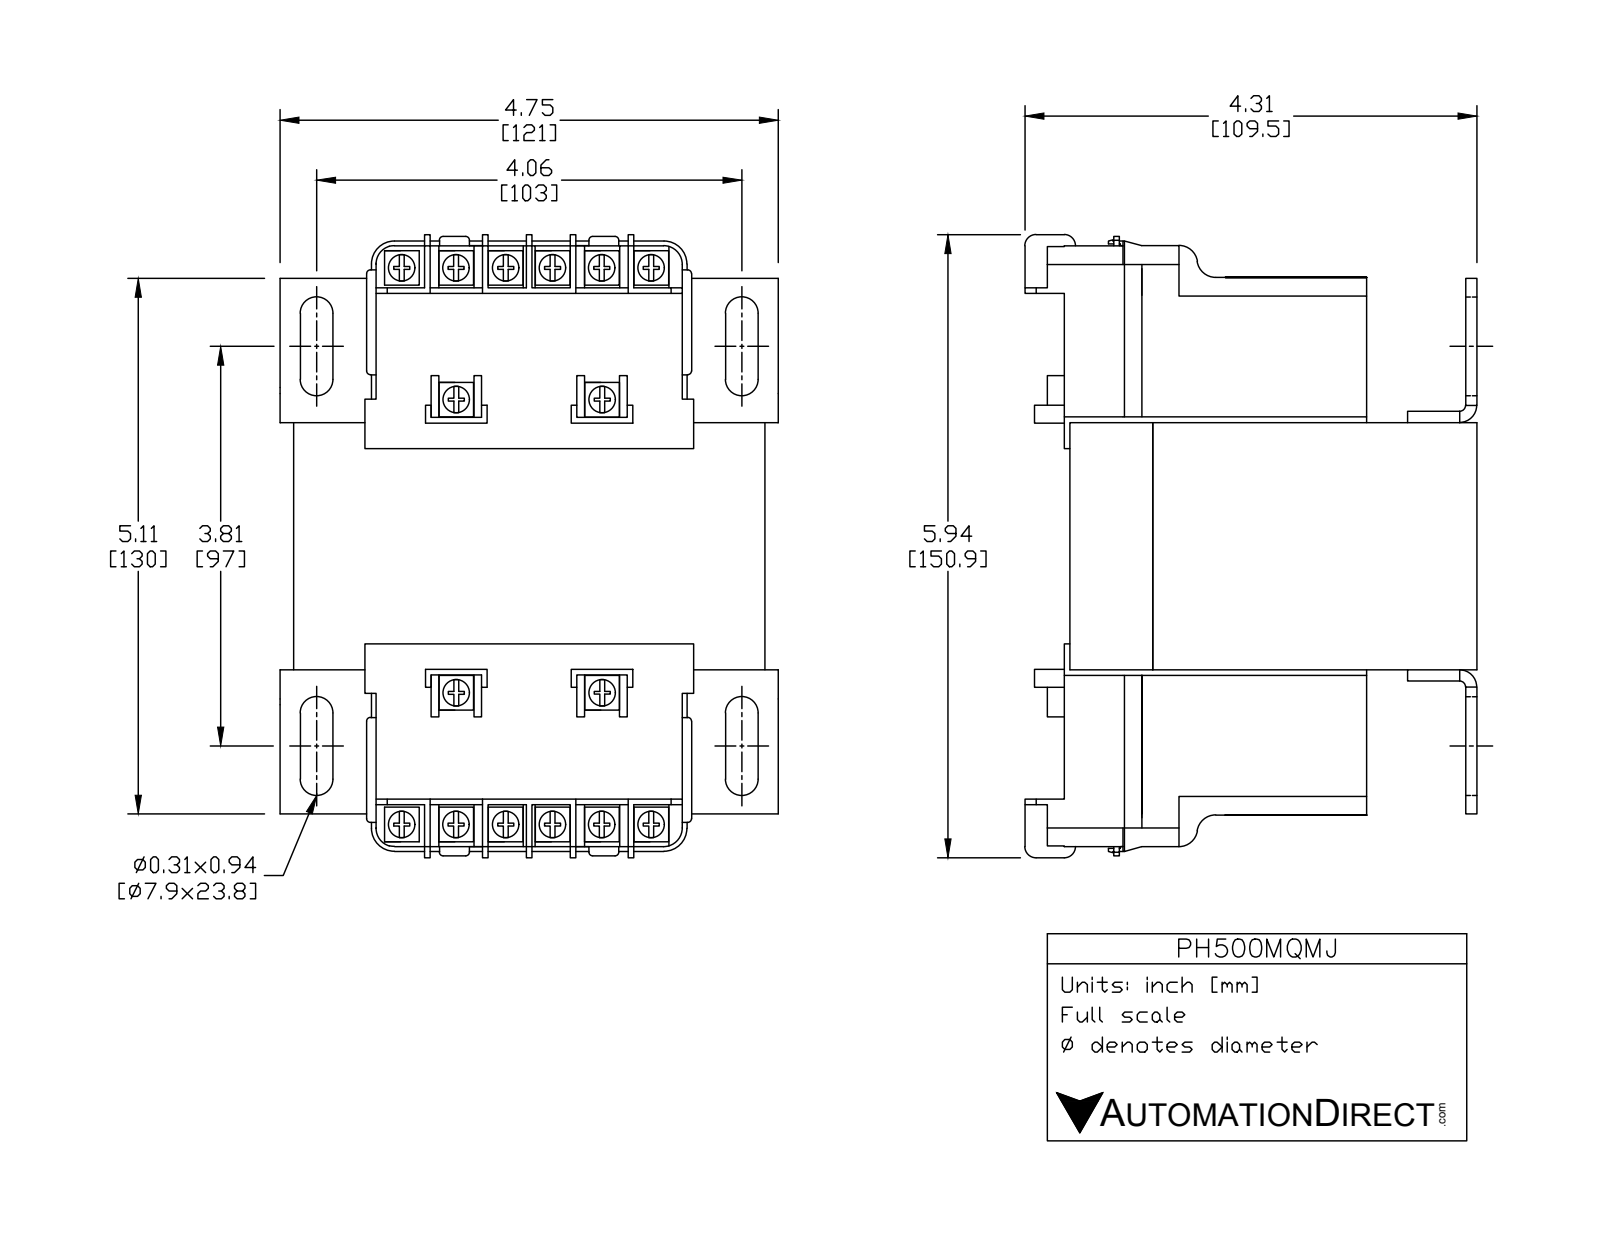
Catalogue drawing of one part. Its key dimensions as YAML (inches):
part_name: "PH500MQMJ"
step_written_by: "SolidWorks 2017 (AUTOMOTIVE_DESIGN)"
units: inches
bodies: {solids: 8, faces: 586, planar: 330, cylindrical: 166, other: 90}
overall_size: [5.823, 4.75, 4.213]
volume: 75.83
surface_area: 250.2
round_holes:
  - {diameter: 0.157, count: 4}
  - {diameter: 0.276, count: 2}
partial_cylinders:
  - {radius: 0.039, count: 84}
  - {radius: 0.197, count: 18}
  - {radius: 0.155, count: 8}
  - {radius: 0.243, count: 4}
  - {radius: 0.062, count: 2}
  - {radius: 0.141, count: 2}
face_to_face_distances: [2.362, 0.187, 2.992, 3.179, 0.63, 3.858, 3.74, 1.22, 3.661, 0.079]
hole_center_spacings: [2.756, 3.931, 4.801, 3.74]
